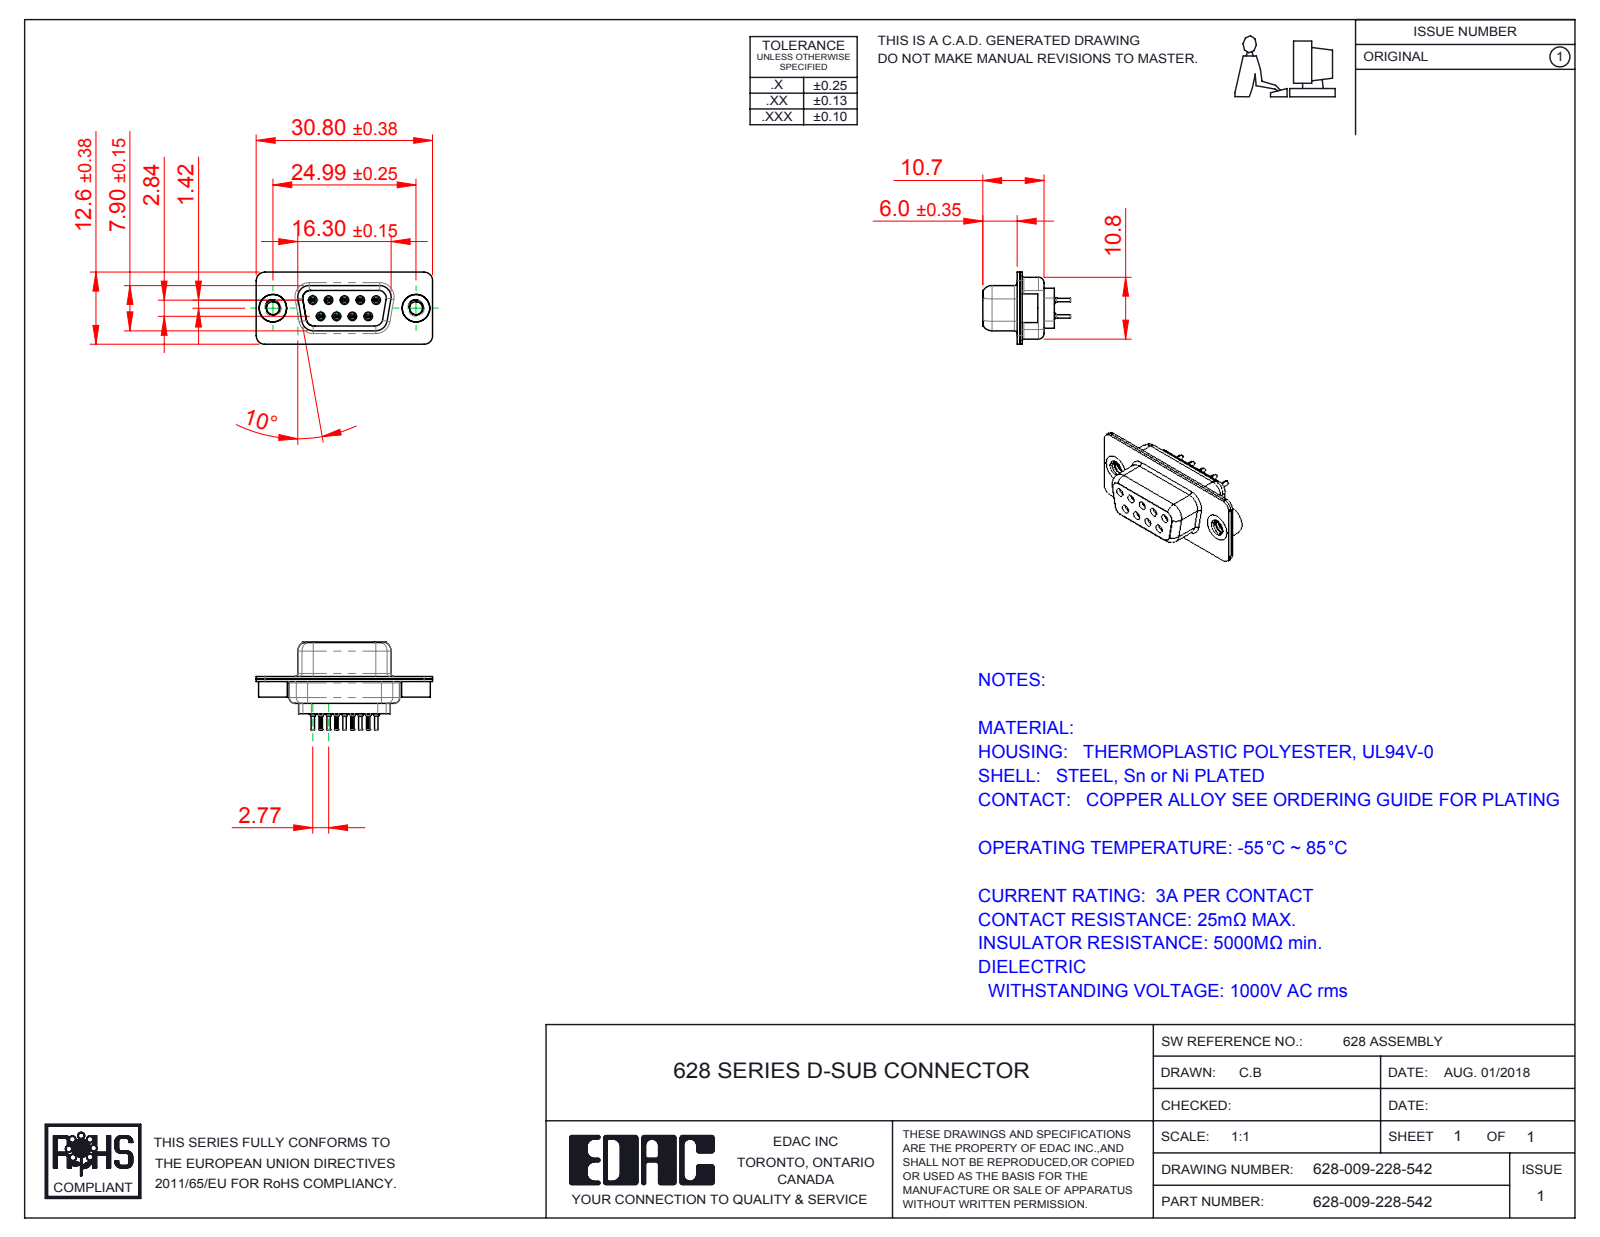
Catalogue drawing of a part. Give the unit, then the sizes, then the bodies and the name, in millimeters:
Units: millimetres
Overall size (bounding box): 30.8 × 15.3 × 12.6
Round holes (diameter × count): ⌀0.2 ×9, ⌀0.8 ×9, ⌀0.9 ×9, ⌀1.1 ×9, ⌀1.6 ×9, ⌀1.7 ×5, ⌀2.26 ×2, ⌀4 ×2, ⌀4.8 ×2
Round bosses / shafts (diameter × count): ⌀2 ×9, ⌀1.5 ×9, ⌀1.2 ×9, ⌀0.6 ×9, ⌀5 ×2, ⌀4.9 ×2
Partial cylindrical surfaces — rounded edges, fillets, slot ends (radius × count): R0.1 ×18, R1.5 ×16, R2 ×12, R0.28 ×9, R1.35 ×7, R0.25 ×4, R0.5 ×4, R0.6 ×4
Main face-to-face distances: 0.45, 0.4, 0.9, 1.9, 8.5, 6.6, 0.5, 1.4, 7.05, 0.85
Hole centre spacings: 3.16, 2.77, 5.54, 5.03, 5.04, 8.31, 7.48, 7.49
Volume: 1 757 mm³ · Surface area: 4 463 mm²
Bodies: 14 solids, 1422 faces (346 planar, 434 cylindrical, 642 other)
Part name (STEP PRODUCT): 628 Contact Row 1_28L; 628 Shell Rear_09 Contacts; 628 Contact Row 2_28L; 628 4-40 Threaded Rivet (+3 more)
STEP written by: SolidWorks 2016 (CONFIG_CONTROL_DESIGN)
